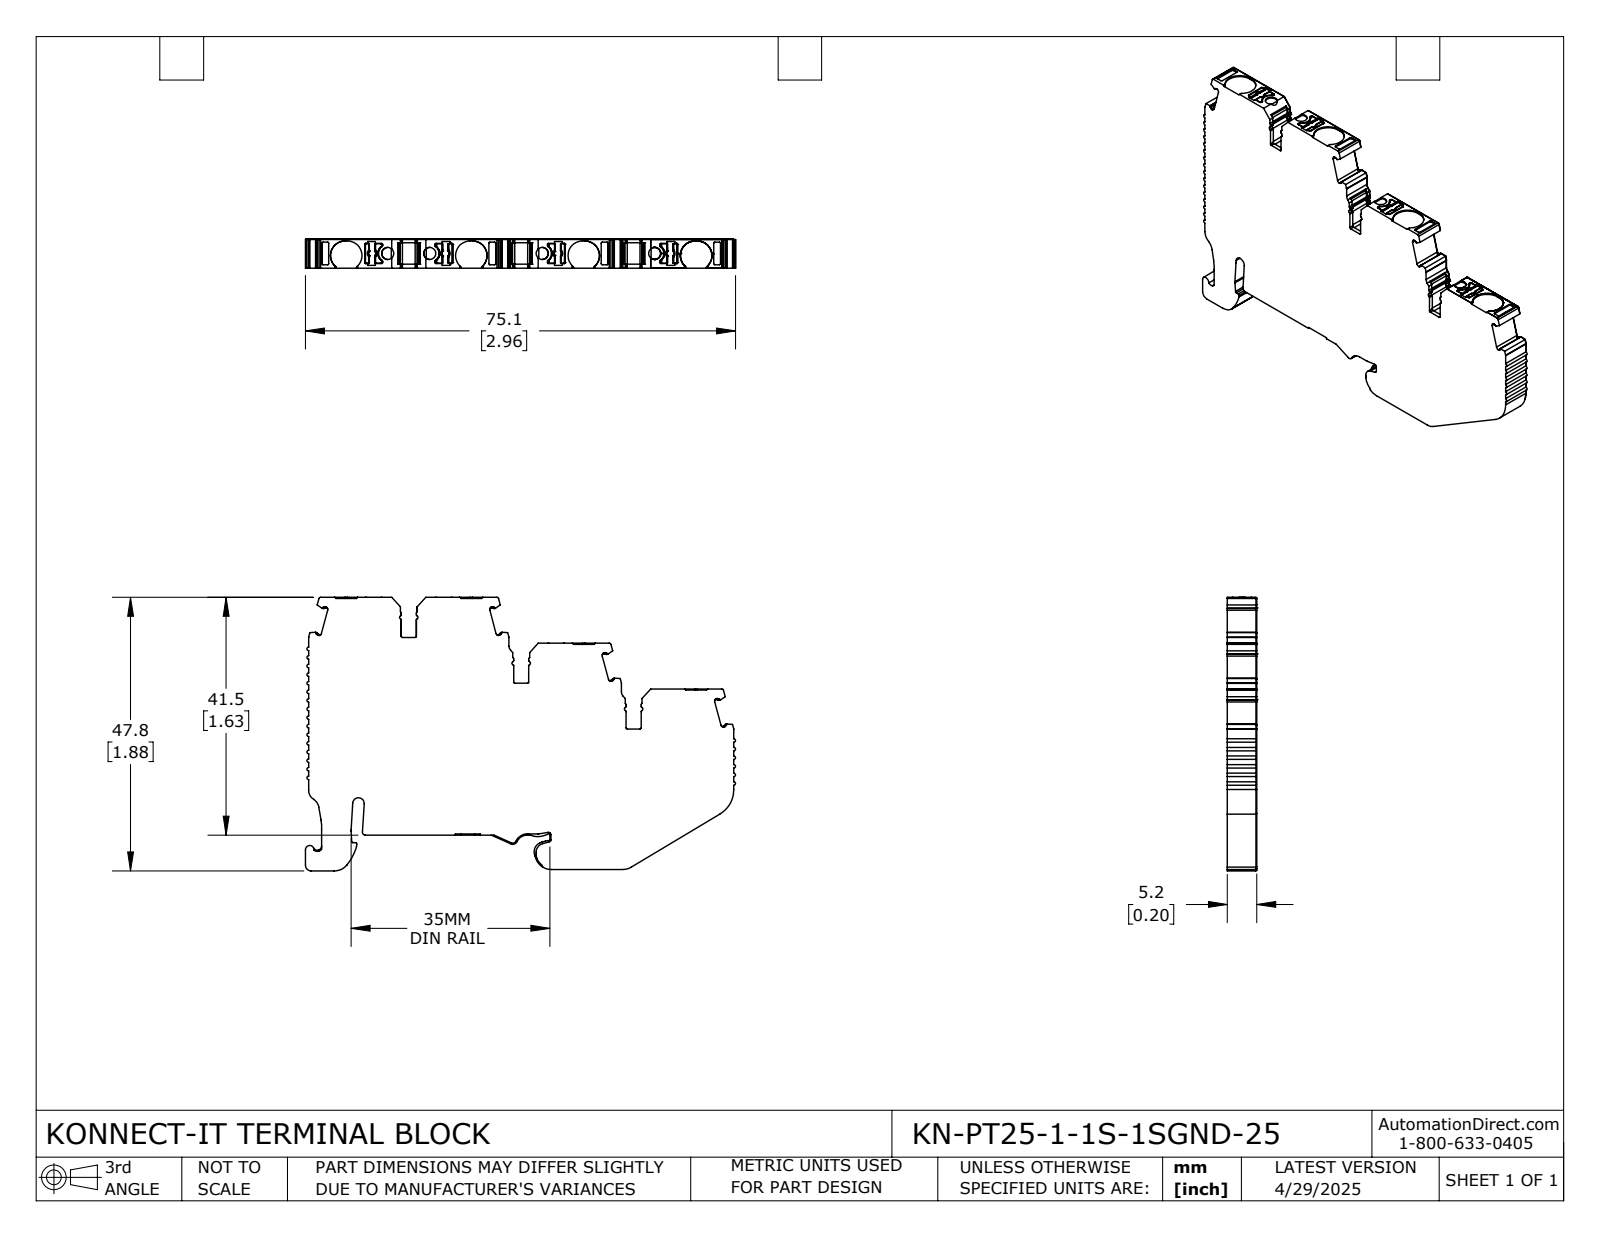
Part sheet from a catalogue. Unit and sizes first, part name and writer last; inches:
Units: inches
Overall size (bounding box): 2.957 × 1.88 × 0.203
Round holes (diameter × count): ⌀0.083 ×4
Partial cylindrical surfaces — rounded edges, fillets, slot ends (radius × count): R0.008 ×92, R0.012 ×60, R0.004 ×35, R0.006 ×16, R0.02 ×16, R0.016 ×15, R0.006 ×8, R0.01 ×8
Main face-to-face distances: 0.203, 0.315, 0.63, 0.236, 0.315, 0.323, 0.079, 0.773, 1.626, 1.311
Hole centre spacings: 0.289, 0.773, 0.773, 1.062, 1.546, 1.835
Volume: 0.814 in³ · Surface area: 10.77 in²
Bodies: 1 solid, 1004 faces (482 planar, 451 cylindrical, 71 other)
Part name (STEP PRODUCT): KN-PT25-1-1S-1SGND-25
STEP written by: SolidWorks 2024 (CONFIG_CONTROL_DESIGN)
